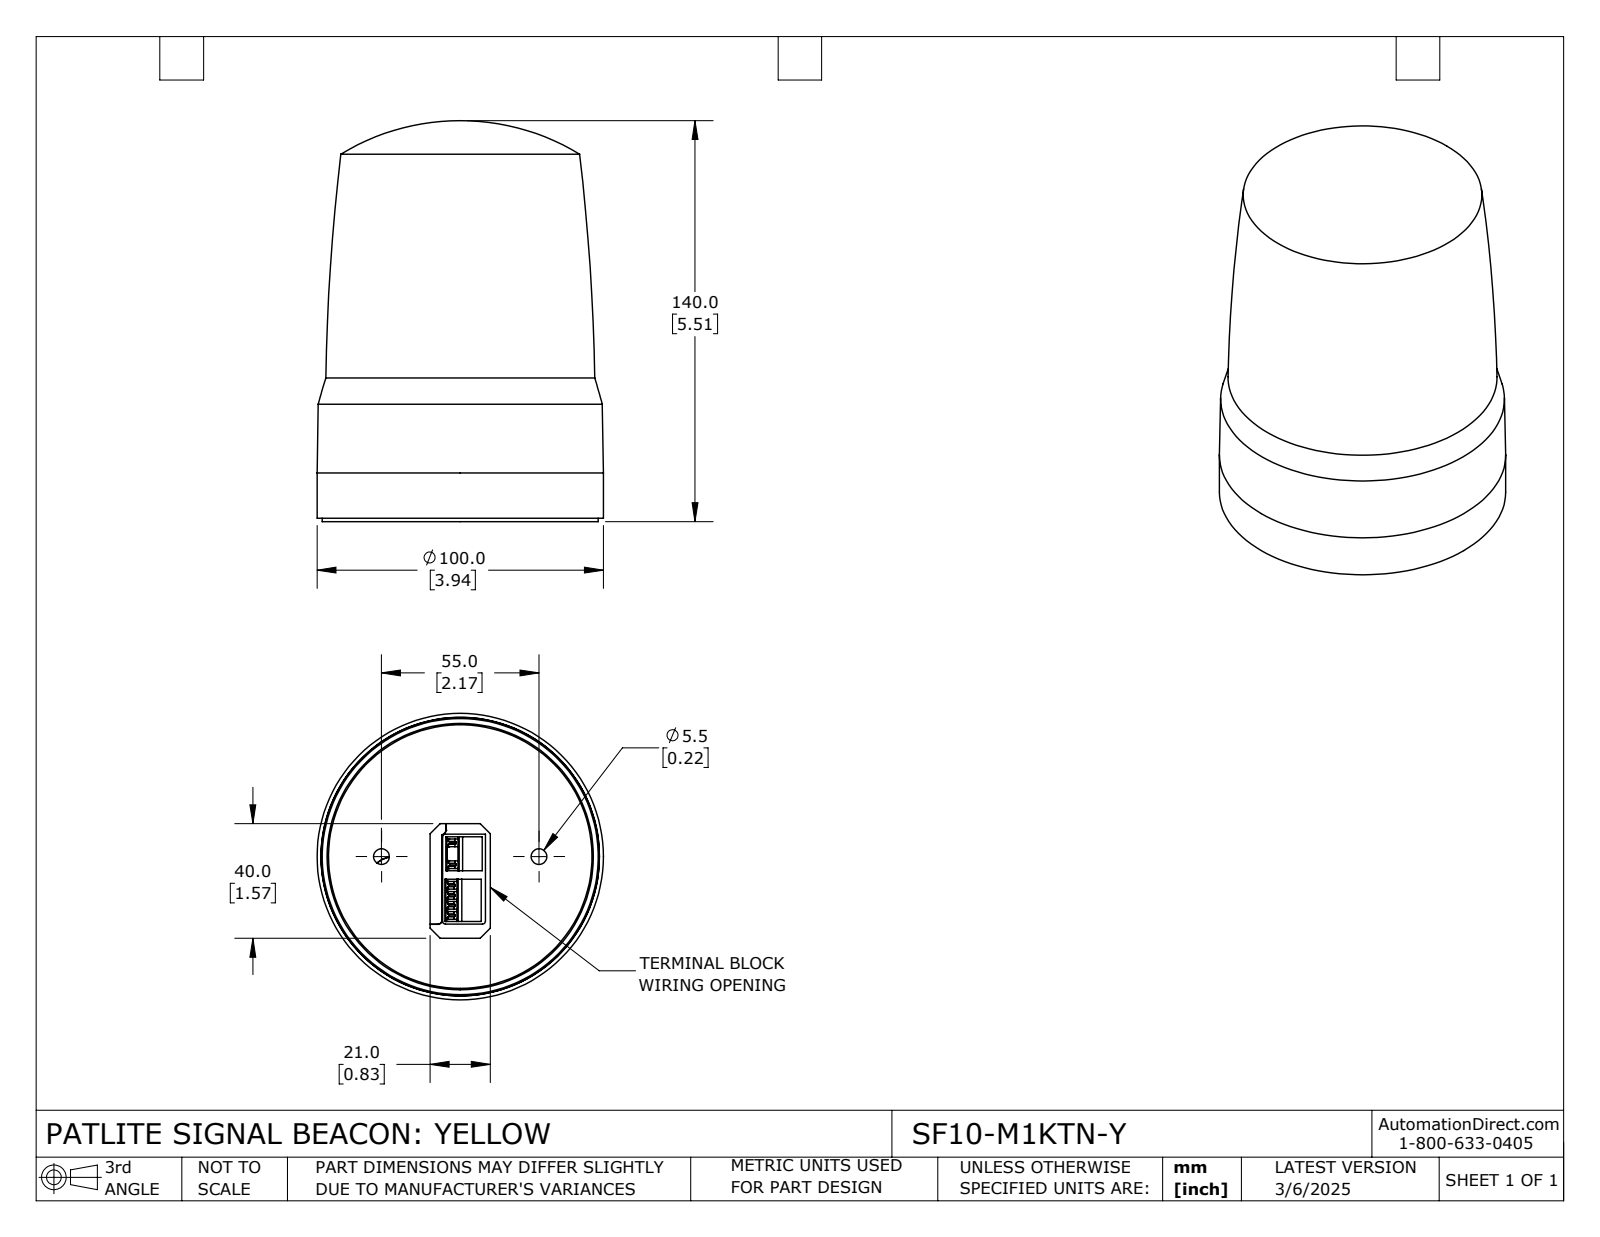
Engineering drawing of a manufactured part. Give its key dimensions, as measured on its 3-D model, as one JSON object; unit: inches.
{"part_name": "SF10-M1KTN-Y", "step_written_by": "SolidWorks 2024 (CONFIG_CONTROL_DESIGN)", "units": "inches", "bodies": {"solids": 2, "faces": 268, "planar": 183, "cylindrical": 29, "other": 56}, "overall_size": [5.512, 3.937, 3.937], "volume_in3": 52.34, "surface_area_in2": 119.3, "round_holes": [[0.217, 2], [0.512, 2], [3.661, 1], [3.764, 1]], "round_bosses_or_shafts": [[3.937, 1], [3.795, 1], [3.72, 1], [3.669, 1], [3.622, 1]], "partial_cylinders_radius": [[0.012, 2], [1.745, 1], [1.762, 1]], "face_to_face_distances": [0.248, 0.579, 0.331, 0.059, 0.272, 0.52, 0.496, 0.124, 0.173, 0.276], "hole_center_spacings": [1.083, 2.165]}
